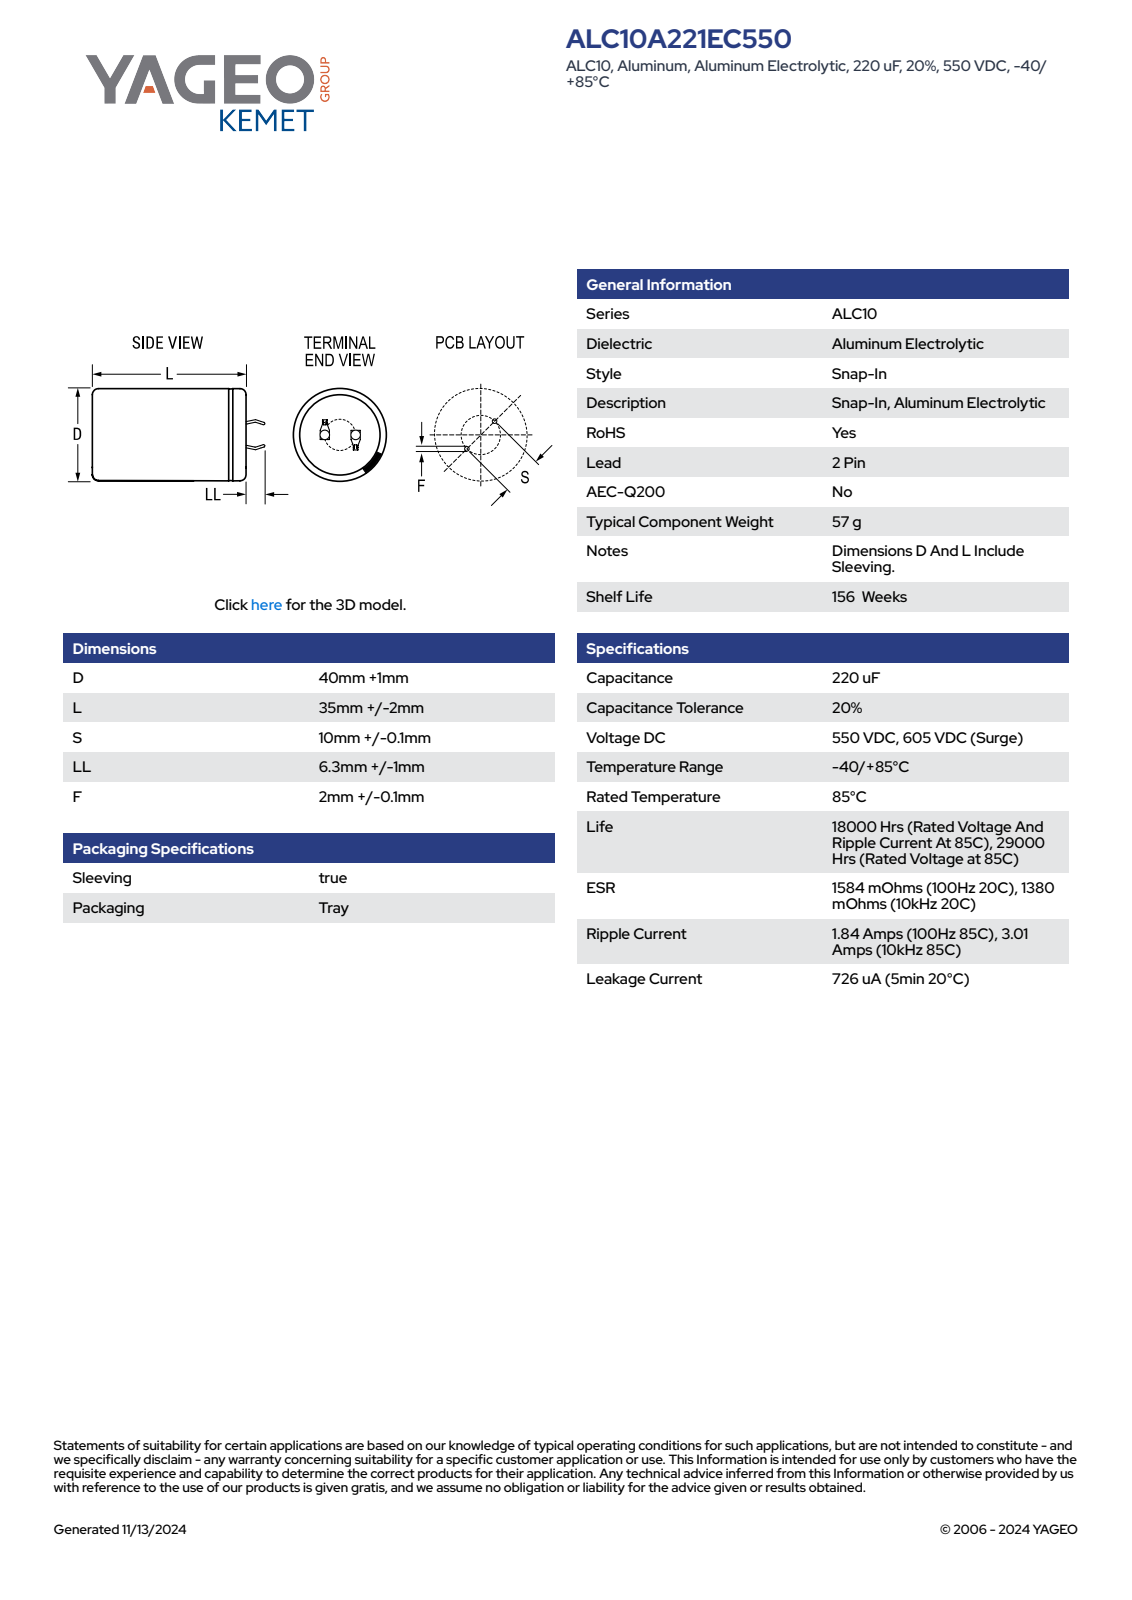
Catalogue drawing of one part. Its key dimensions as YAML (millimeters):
part_name: "CARS_K2P_40X35_D41L37S10LL7.3F2.1"
step_written_by: "SolidWorks 2014 (AUTOMOTIVE_DESIGN)"
units: millimeters
bodies: {solids: 1, faces: 100, planar: 52, cylindrical: 9, other: 39}
overall_size: [44.29, 41, 41]
volume: 48065
surface_area: 7389
round_holes:
  - {diameter: 36.28, count: 1}
round_bosses_or_shafts:
  - {diameter: 41, count: 1}
partial_cylinders:
  - {radius: 20.49, count: 1}
face_to_face_distances: [36.99, 0.6, 37.49, 0.5, 7.08, 7.64, 0.75, 1.35, 7.68, 6.48]
